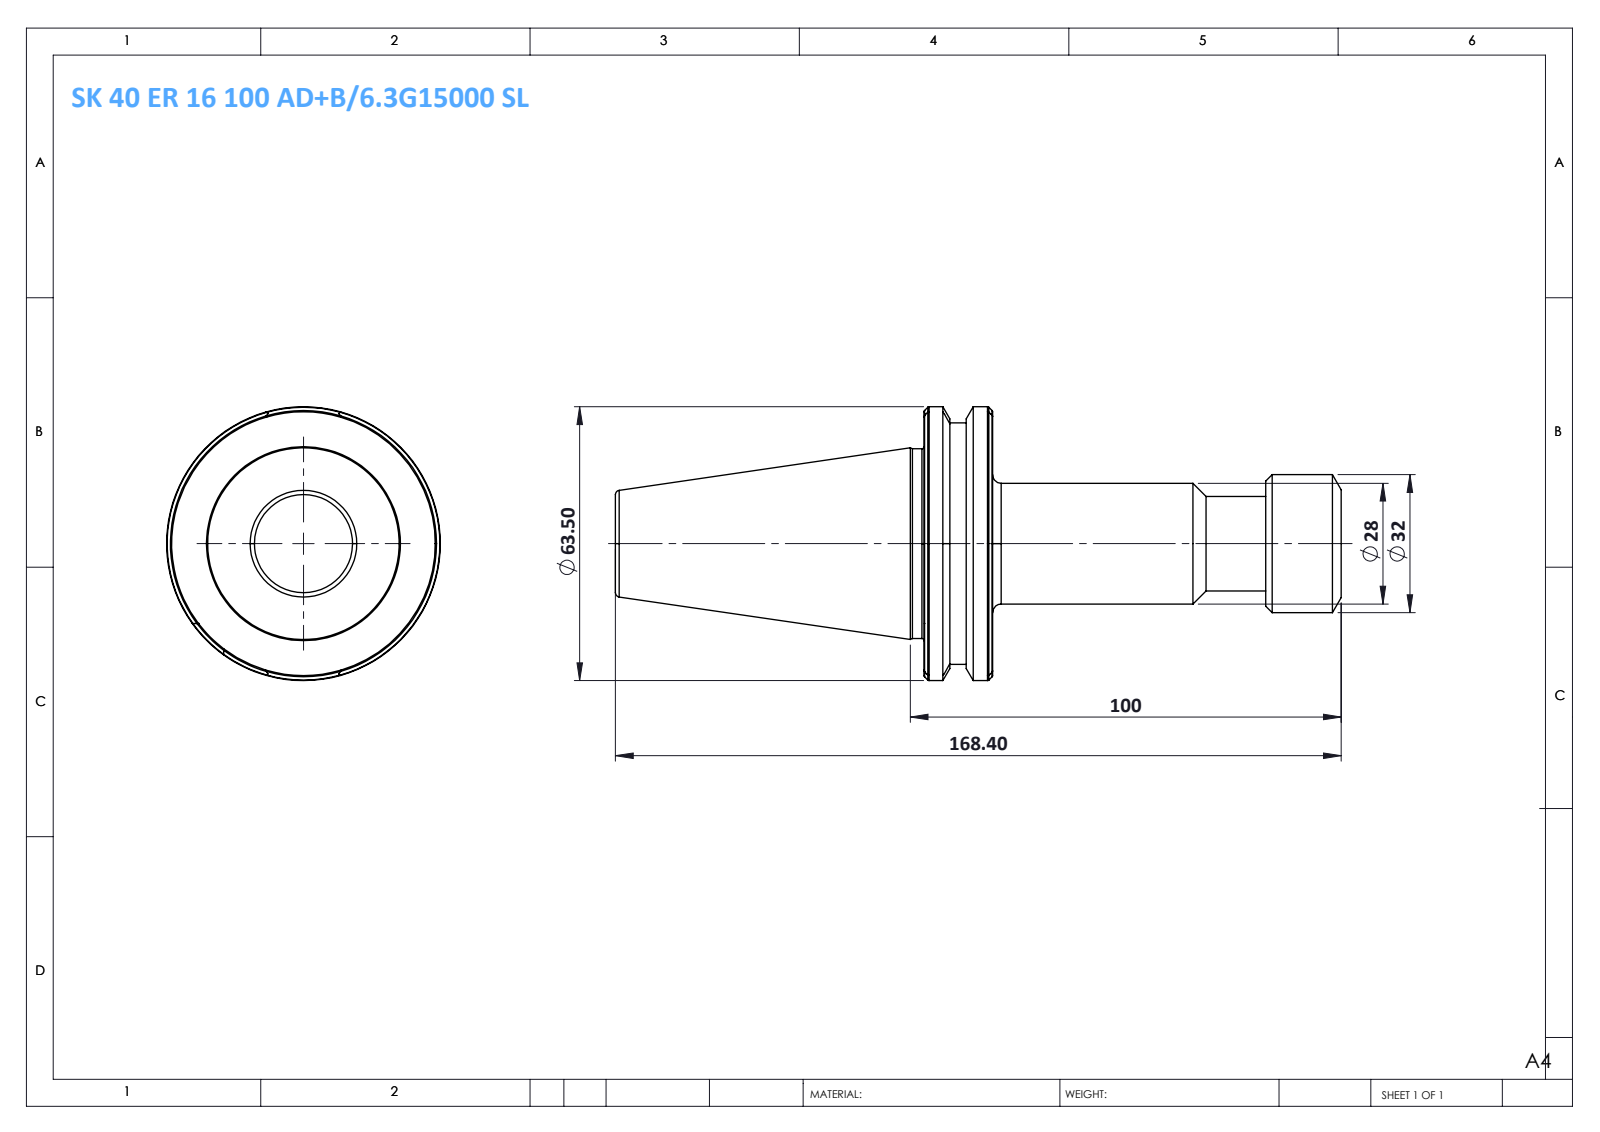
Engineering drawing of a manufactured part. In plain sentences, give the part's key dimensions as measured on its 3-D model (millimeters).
The part is named "SK 40 ER 16 100 AD-6.3G15000 SL". Its 3-D file was written by "SolidWorks 2014 (CONFIG_CONTROL_DESIGN)". It is 1 solid with 89 faces: 7 planar, 14 cylindrical and 68 other. Overall it measures 168.4 by 63.5 by 63.5 millimeters. Its volume is 166 152 cubic millimeters and its surface area 24 362 square millimeters. Round bosses or shafts: 1 of diameter 63.5, 1 of diameter 56, 1 of diameter 44, 1 of diameter 32, 1 of diameter 28, 1 of diameter 21.9. The main face-to-face distances are 15.9, 80.9, 96.8, 168.4, 87.5, 71.6, 17.5, 63.4, 79.3, 150.9.
